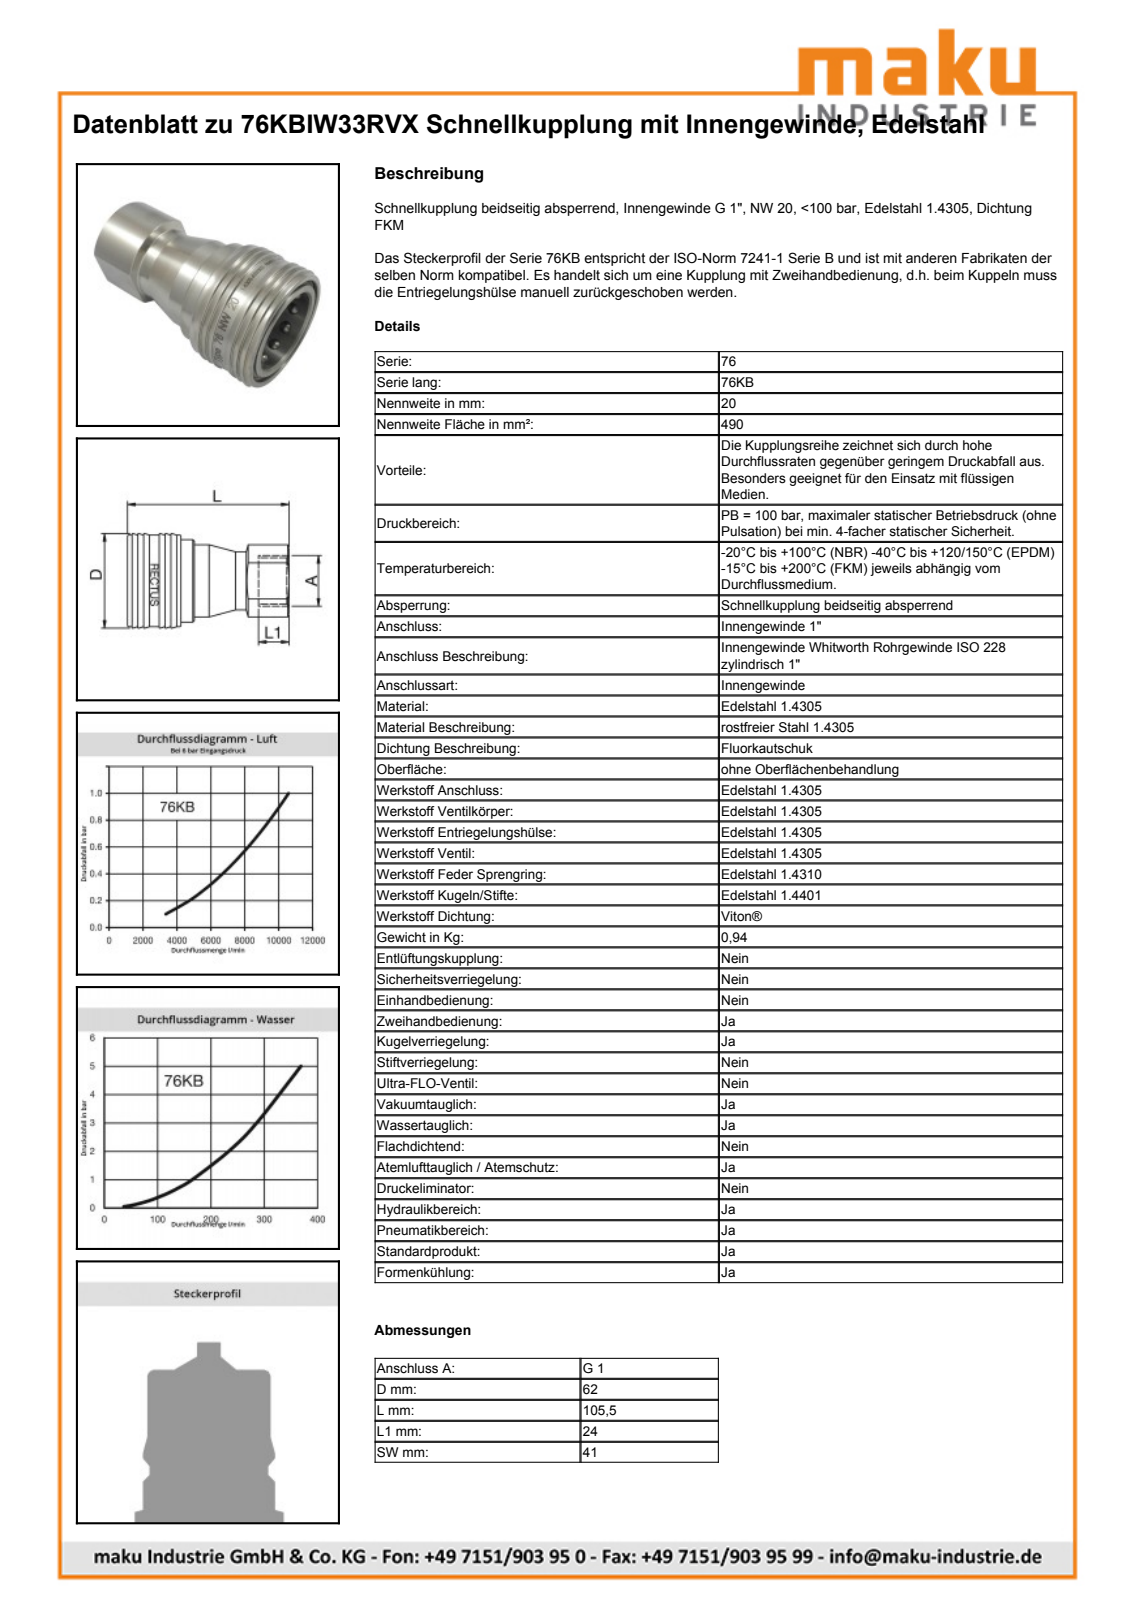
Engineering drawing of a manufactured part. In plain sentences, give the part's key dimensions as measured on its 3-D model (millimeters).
The part is named "D110521". Its 3-D file was written by "Autodesk Inventor 2013 (AUTOMOTIVE_DESIGN)". It is 3 solids with 868 faces: 303 planar, 94 cylindrical and 471 other. Overall it measures 105.6 by 62 by 62 millimeters. Its volume is 184 992 cubic millimeters and its surface area 39 484 square millimeters. Round holes: 1 of diameter 33.25, 1 of diameter 49.5, 1 of diameter 54, 1 of diameter 54.4. Round bosses or shafts: 1 of diameter 60, 1 of diameter 49, 1 of diameter 47.3, 1 of diameter 38. Partial cylindrical surfaces (rounded edges, fillets, slot ends): 1 of radius 23.15, 1 of radius 29.9. The main face-to-face distances are 81.6, 41, 46.6, 35, 38, 8.6, 43.6, 3.5, 50.1, 12.1.
